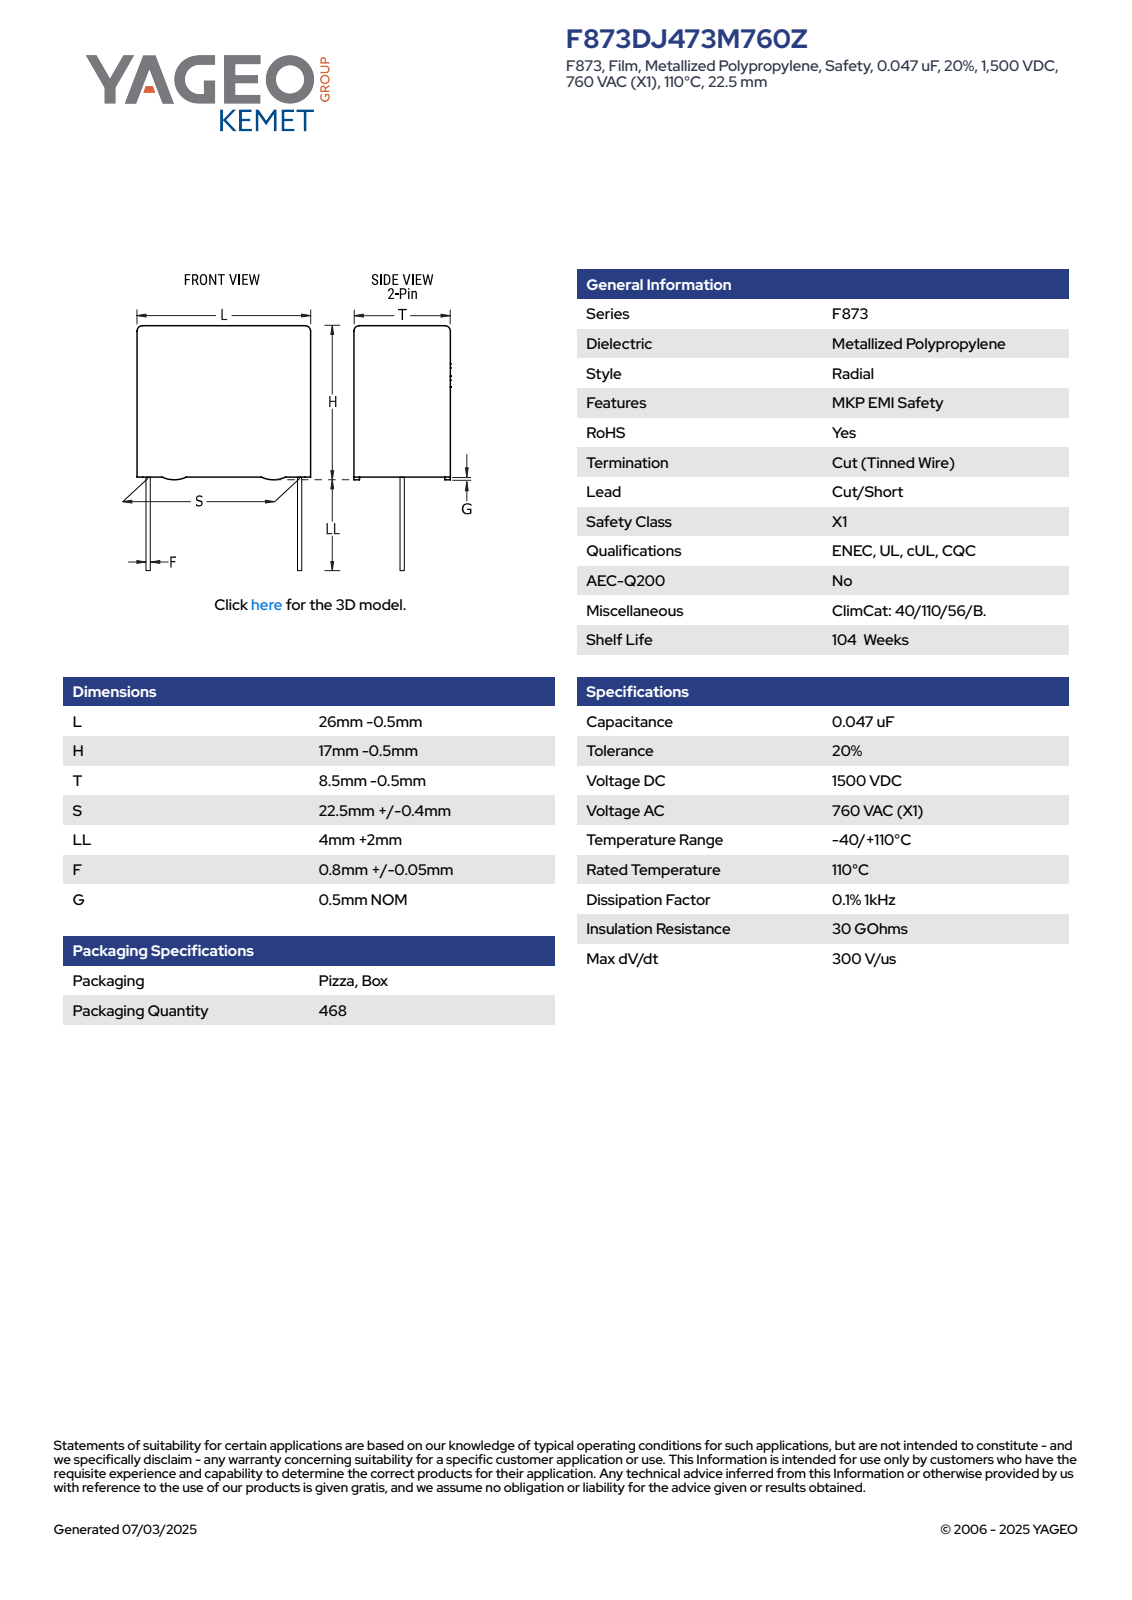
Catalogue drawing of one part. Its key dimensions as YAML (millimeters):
part_name: "CFR_RBG_26X17X8.5_L25.5H16.5T8S22.5LL6F0.85G0.5"
step_written_by: "SolidWorks 2014 (AUTOMOTIVE_DESIGN)"
units: millimeters
bodies: {solids: 4, faces: 89, planar: 81, cylindrical: 8, other: 0}
overall_size: [25.5, 22.5, 8.01]
volume: 3272
surface_area: 1588
round_bosses_or_shafts:
  - {diameter: 0.85, count: 2}
partial_cylinders:
  - {radius: 0.5, count: 4}
face_to_face_distances: [8, 16, 25.5, 8.01, 0.46, 7.54, 16.5, 0.5, 0.47, 7.08]
